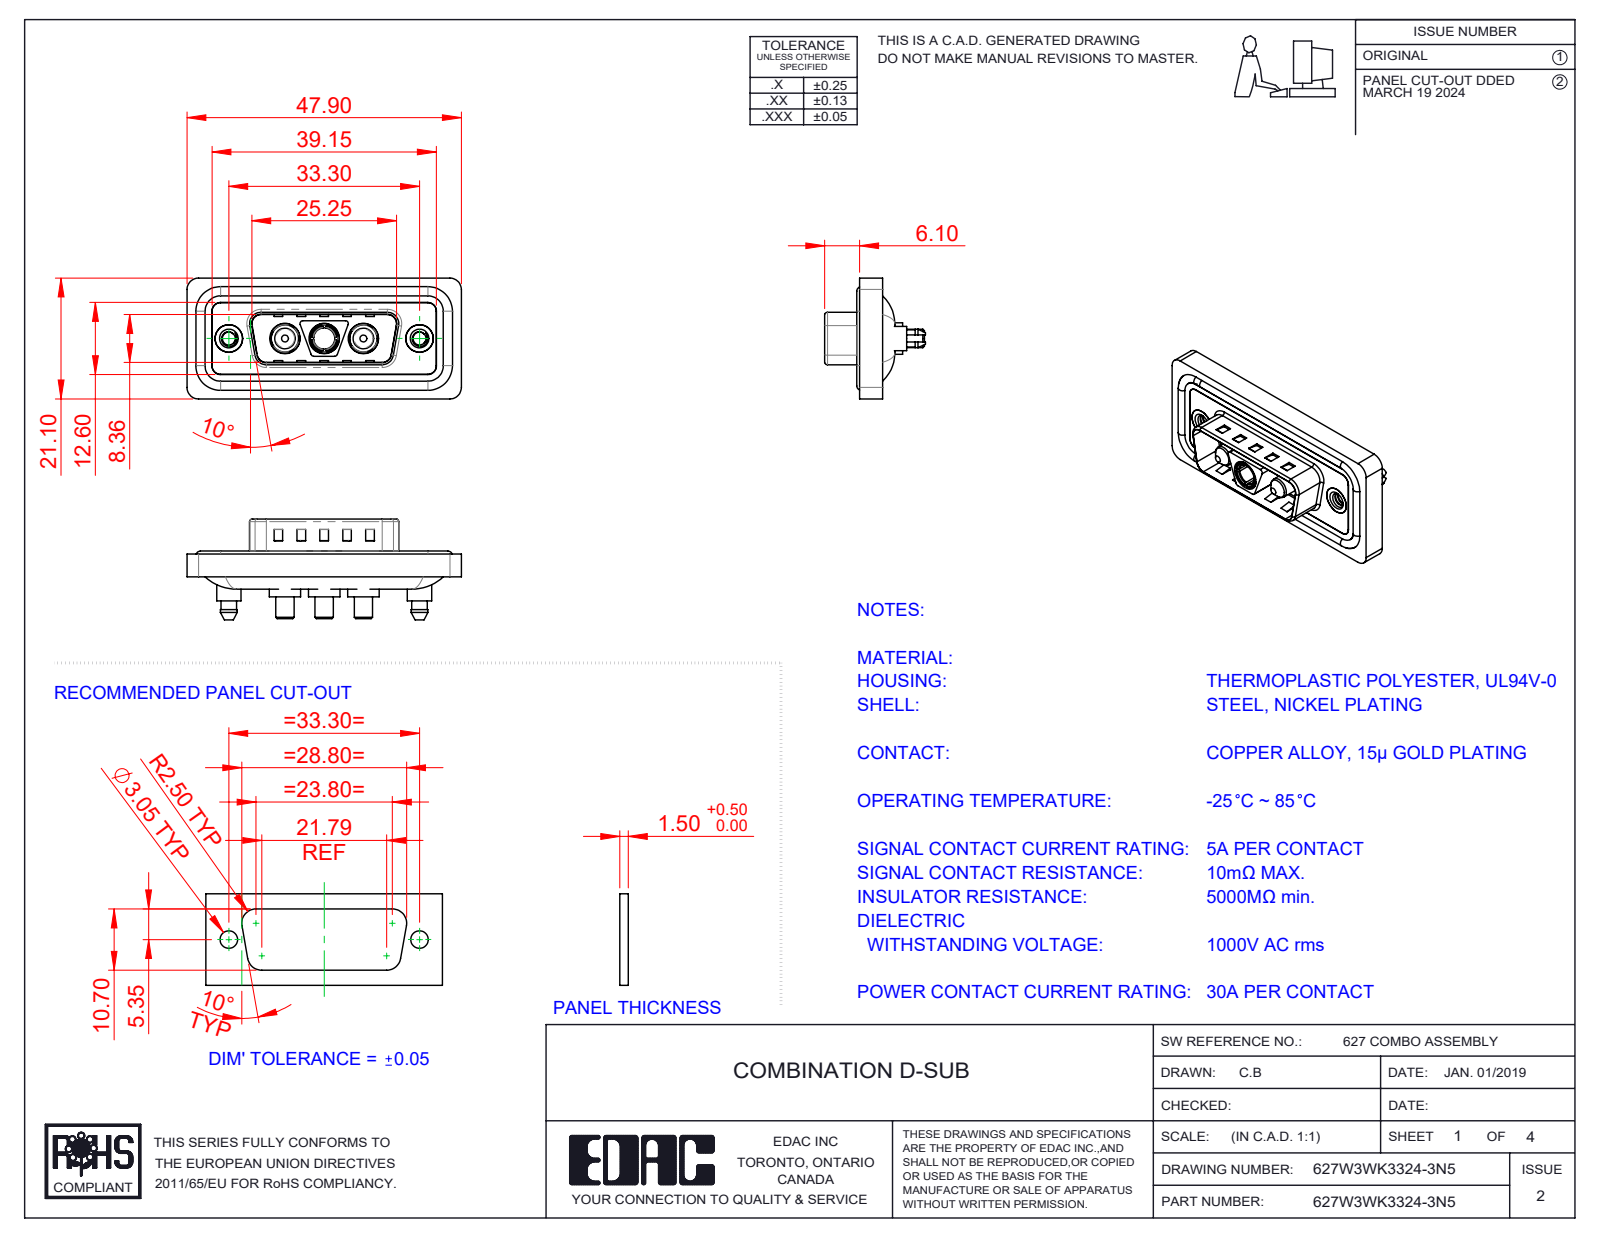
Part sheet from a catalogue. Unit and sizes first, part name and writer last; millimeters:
Units: millimetres
Overall size (bounding box): 47.9 × 21.1 × 17.6
Round holes (diameter × count): ⌀4.85 ×3, ⌀5.3 ×3, ⌀2.26 ×2, ⌀4 ×2, ⌀4.8 ×2, ⌀5 ×2, ⌀3.7 ×1
Round bosses / shafts (diameter × count): ⌀1.6 ×4, ⌀5.5 ×3, ⌀5.2 ×3, ⌀4.75 ×3, ⌀3.75 ×3, ⌀3.2 ×3, ⌀5.4 ×2, ⌀4.9 ×2
Partial cylindrical surfaces — rounded edges, fillets, slot ends (radius × count): R1.5 ×28, R2 ×20, R0.5 ×12, R1.6 ×10, R0.25 ×4, R0.6 ×4, R0.65 ×4, R0.9 ×4
Main face-to-face distances: 0.4, 1.1, 1.5, 0.5, 3.1, 1.6, 2.9, 4, 0.7, 0.82
Hole centre spacings: 6.85, 9.8, 16.65, 23.5, 13.7, 33.3
Volume: 5 843 mm³ · Surface area: 9 474 mm²
Bodies: 13 solids, 659 faces (247 planar, 282 cylindrical, 130 other)
Part name (STEP PRODUCT): 627Combo Shell Front_15 Contacts; 627W3WK3324-3N5; Power Socket_30A S; 627Combo Waterproof Housing_15 Contacts (+4 more)
STEP written by: SolidWorks 2023 (CONFIG_CONTROL_DESIGN)
